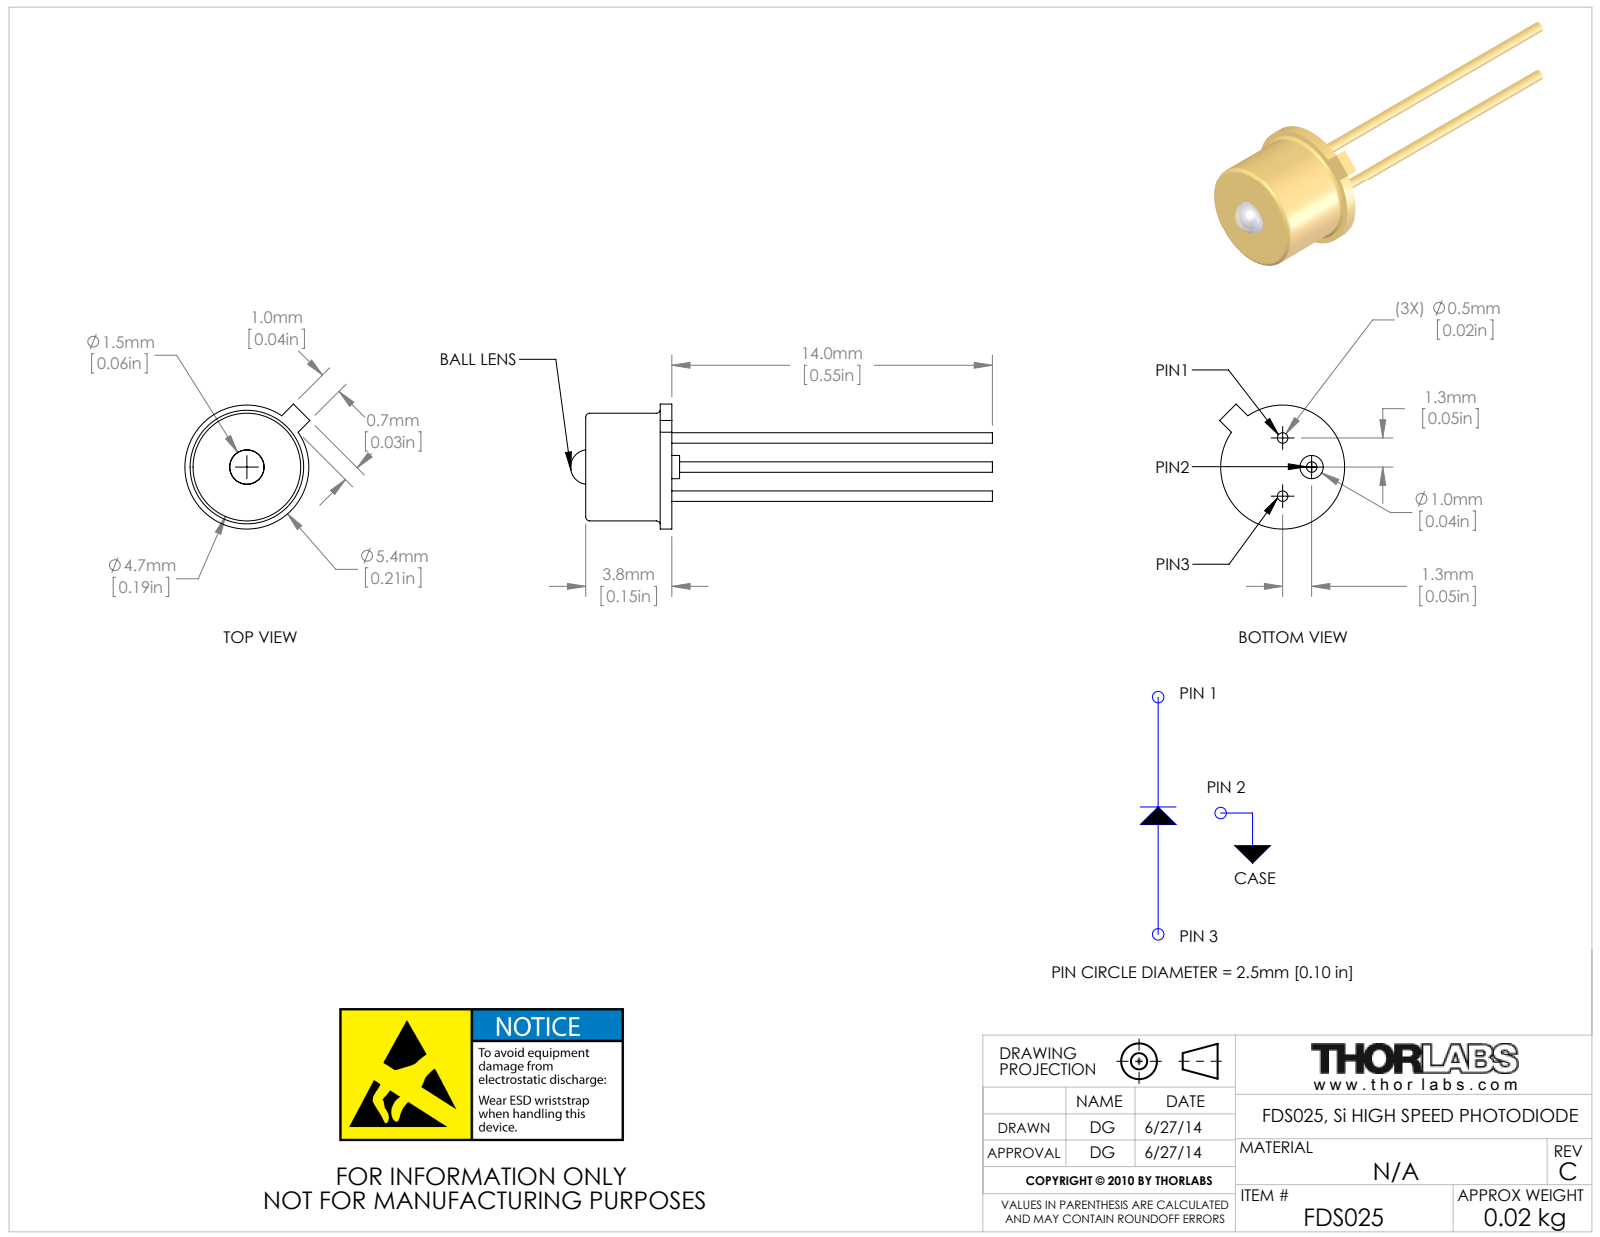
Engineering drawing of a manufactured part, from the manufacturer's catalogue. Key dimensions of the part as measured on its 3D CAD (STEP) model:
Part name (STEP PRODUCT): TTN019843-E0W
STEP written by: SolidWorks 2012 (AUTOMOTIVE_DESIGN)
Units: inches
Bodies: 2 solids, 38 faces (13 planar, 17 cylindrical, 8 other)
Overall size (bounding box): 0.725 × 0.215 × 0.215
Volume: 0.002 in³ · Surface area: 0.371 in²
Round holes (diameter × count): ⌀0.059 ×1, ⌀0.173 ×1
Round bosses / shafts (diameter × count): ⌀0.018 ×3, ⌀0.213 ×1, ⌀0.185 ×1, ⌀0.04 ×1
Main face-to-face distances: 0.02, 0.148, 0.128, 0.142, 0.122, 0.013, 0.033, 0.156, 0.161, 0.538
